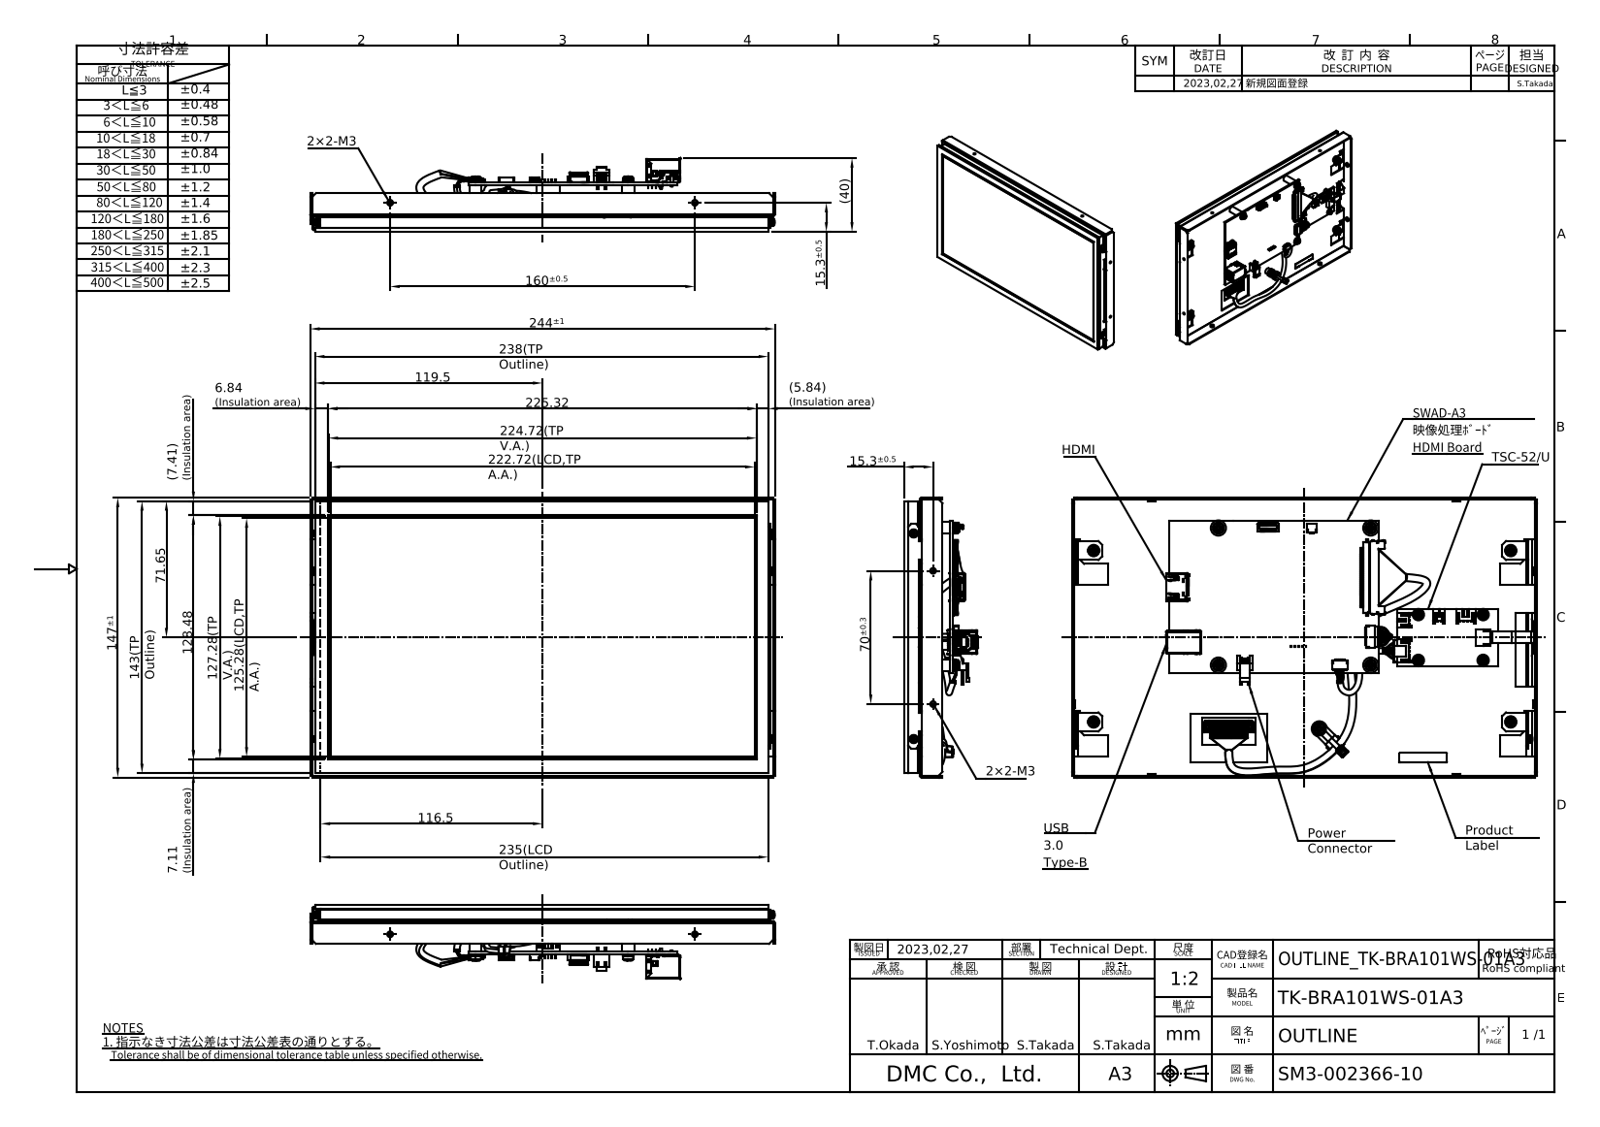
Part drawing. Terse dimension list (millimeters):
name: HP_TK-BRA101WS-01A3
written by: Autodesk Inventor 2020 (AUTOMOTIVE_DESIGN)
unit: mm
bodies: 3 solids, 11597 faces (9008 planar, 2164 cylindrical, 425 other)
size: 244 × 147 × 38.76
volume: 315 622 mm³; area: 264 360 mm²
holes: 13× ⌀2.46, 6× ⌀0.6, 4× ⌀2.11, 4× ⌀3, 4× ⌀3.5, 4× ⌀6, 4× ⌀8, 2× ⌀0.5, 2× ⌀3.2, 1× ⌀2.1, 1× ⌀4, 1× ⌀7
bosses: 40× ⌀0.37, 40× ⌀0.31, 10× ⌀3, 9× ⌀6.2, 9× ⌀6, 9× ⌀5.5, 6× ⌀4, 5× ⌀0.55
rounds: 244× R0.1, 127× R0.2, 94× R0.15, 62× R0.3, 33× R0.5, 26× R0.25, 24× R0.6, 20× R0.17
face distances: 1, 7.46, 0.8, 8.26, 1.8, 9.26, 5.36, 2.1, 7.16, 6.16
hole spacings: 1, 2, 3, 4, 24, 34, 41.62, 72
